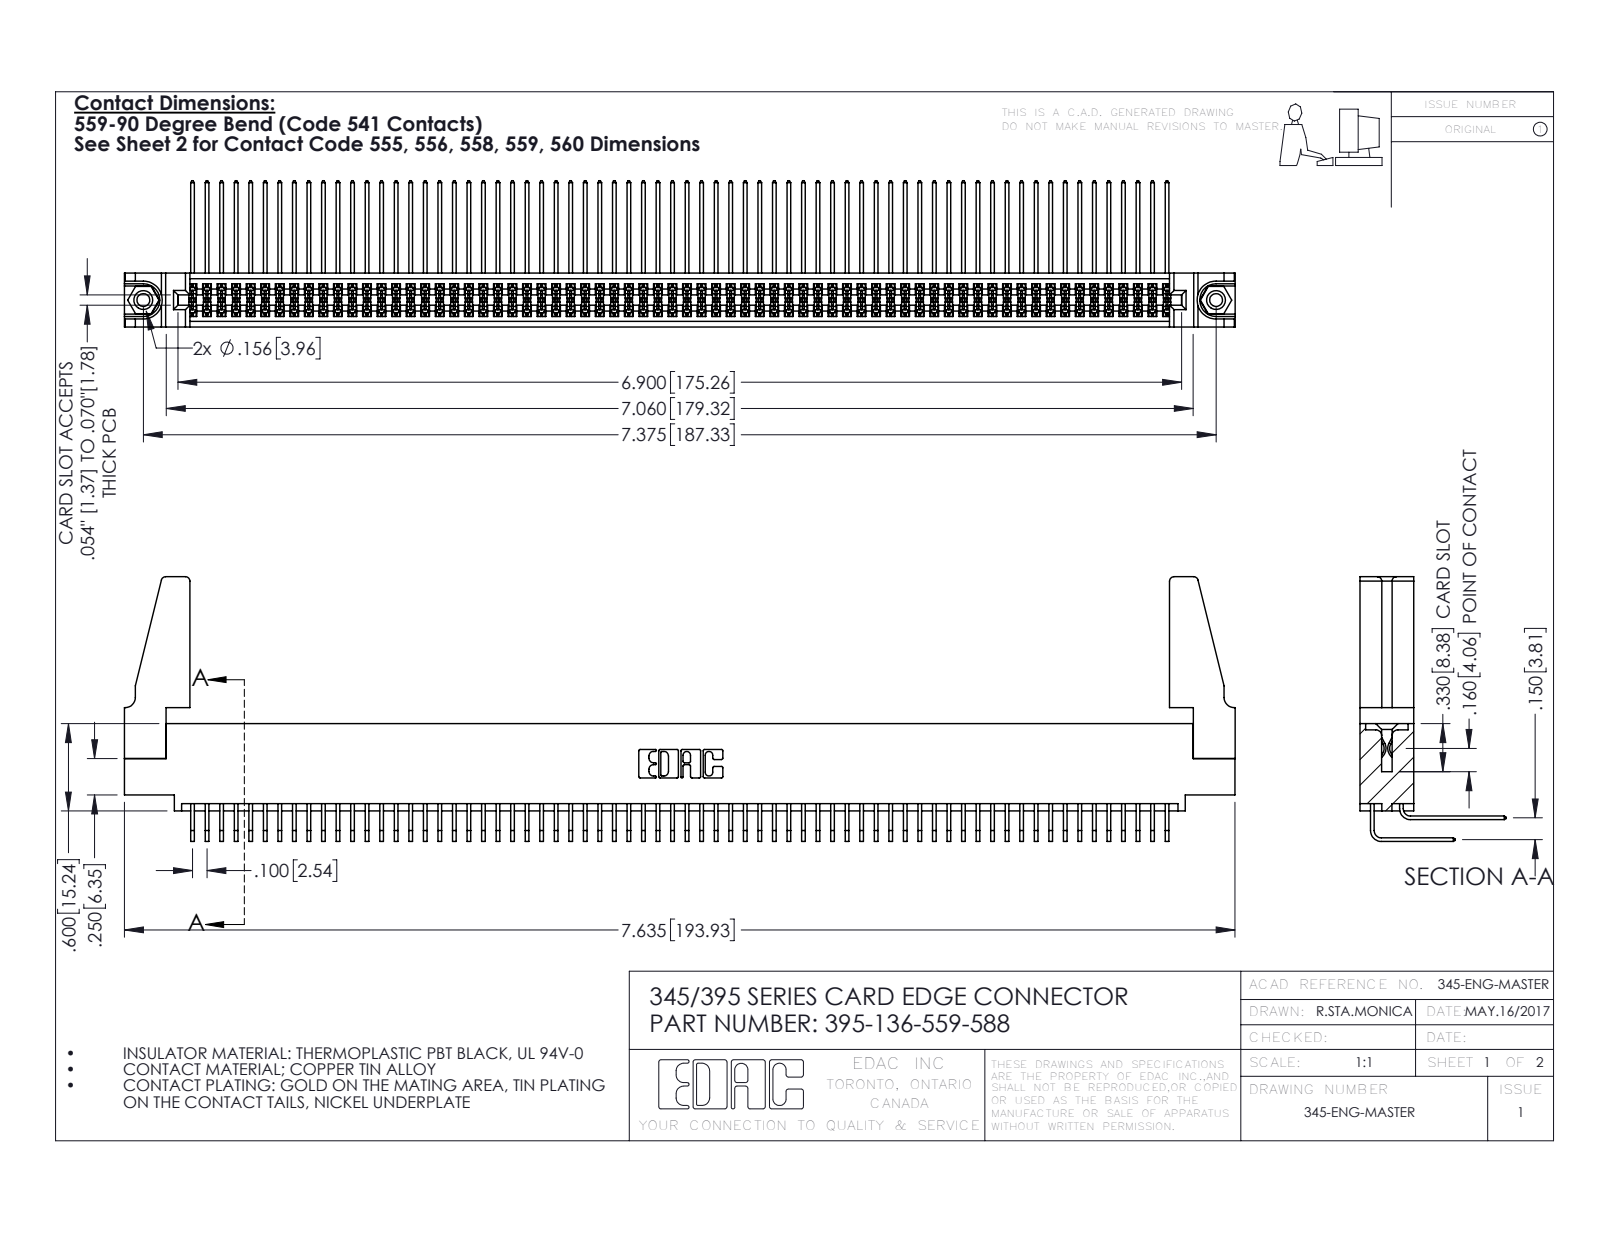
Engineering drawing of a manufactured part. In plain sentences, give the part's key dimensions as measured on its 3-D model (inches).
The part is named "395-136-559-588; 345-250-001_345-250-001-102; 345-292-001_558 559 Tail - 1; 345-220-078_345-220-088 (+2 more)". Its 3-D file was written by "SolidWorks 2016 (CONFIG_CONTROL_DESIGN)". It is 141 solids with 7326 faces: 4916 planar, 2394 cylindrical and 16 other. Overall it measures 7.636 by 1.819 by 1.005 inches. Its volume is 1.406 cubic inches and its surface area 56.83 square inches. Round holes: 2 of diameter 0.089, 2 of diameter 0.125, 2 of diameter 0.156, 1 of diameter 0.064. Round bosses or shafts: 2 of diameter 0.155. Partial cylindrical surfaces (rounded edges, fillets, slot ends): 272 of radius 0.006, 22 of radius 0.01, 8 of radius 0.03, 6 of radius 0.007, 6 of radius 0.031, 3 of radius 0.026, 2 of radius 0.014, 2 of radius 0.019. The main face-to-face distances are 0.072, 0.298, 0.37, 0.098, 0.272, 0.025, 0.2, 0.225, 0.175, 0.15. The hole center spacings are 0.27, 7.139, 7.375.
